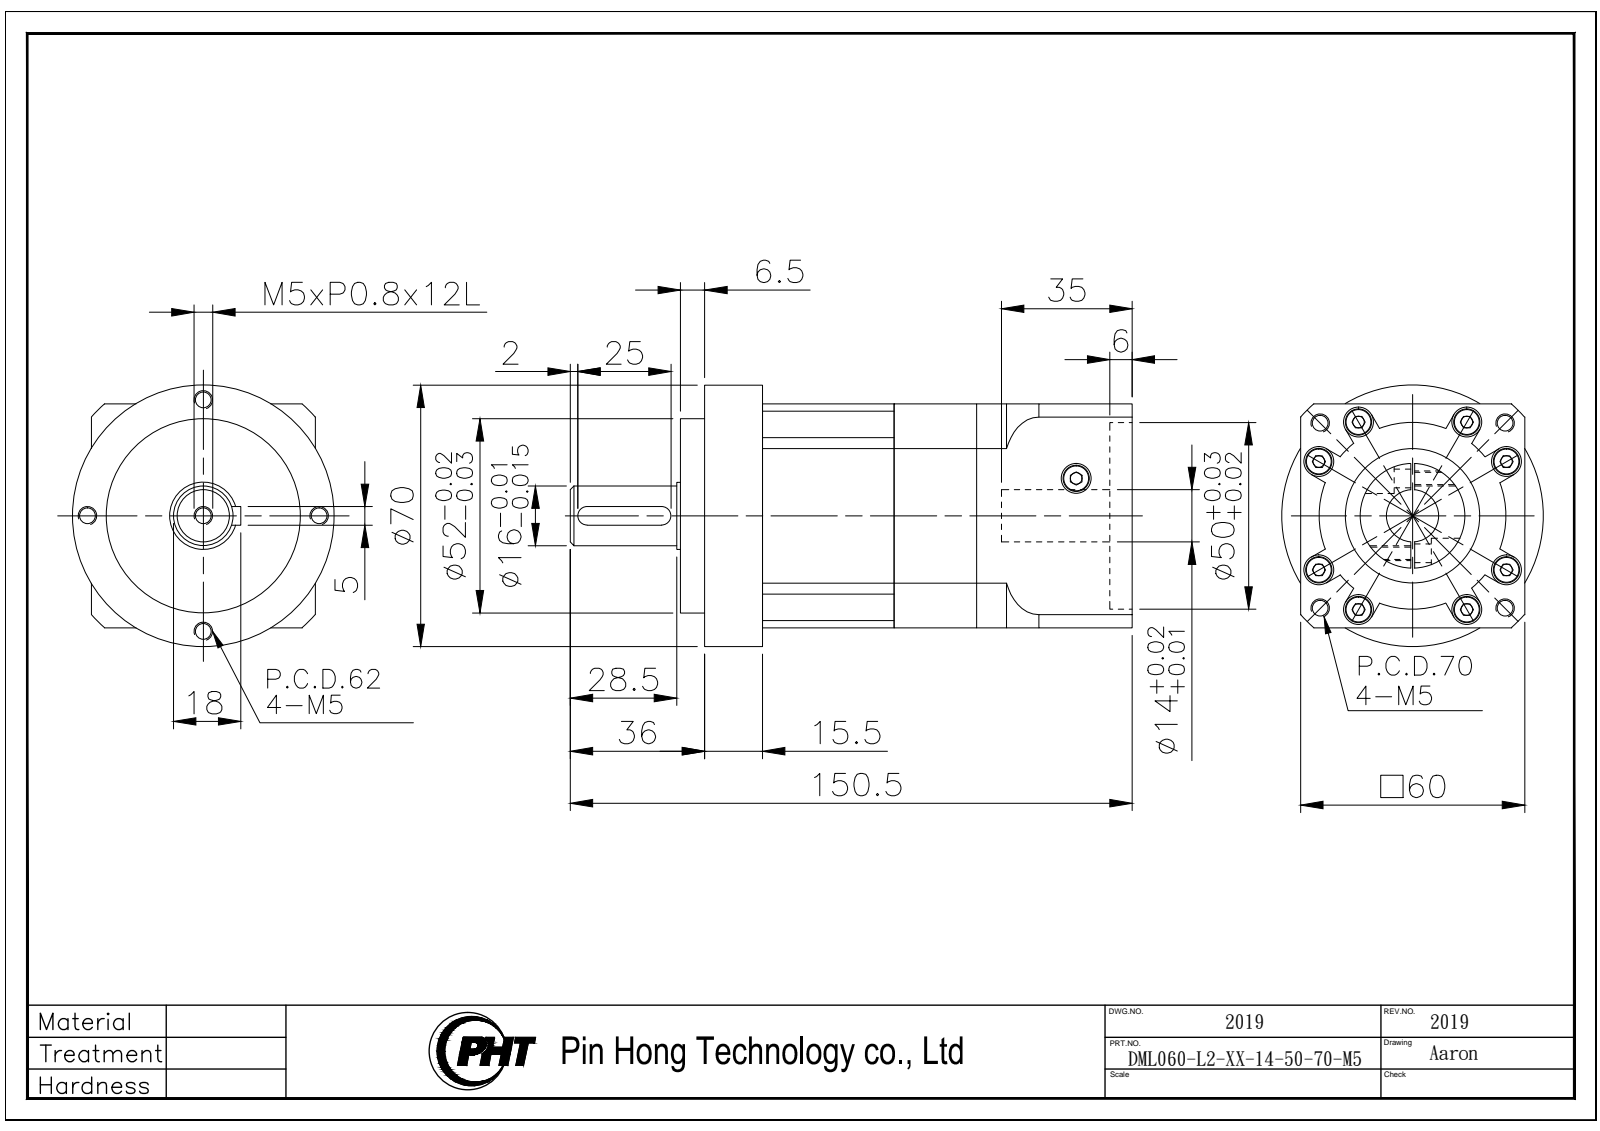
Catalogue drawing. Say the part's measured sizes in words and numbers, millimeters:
The part is named "DML060-L2-XX-14-50-70-M5_2019". Its 3-D file was written by "SolidWorks 2016 (AUTOMOTIVE_DESIGN)". It is 4 solids with 294 faces: 130 planar, 124 cylindrical and 40 other. Overall it measures 150.5 by 70 by 70 millimeters. Its volume is 370 744 cubic millimeters and its surface area 73 760 square millimeters. Round holes: 10 of diameter 8, 9 of diameter 4.2, 8 of diameter 4.5, 1 of diameter 14, 1 of diameter 36. Round bosses or shafts: 8 of diameter 7, 1 of diameter 70, 1 of diameter 52, 1 of diameter 28, 1 of diameter 18, 1 of diameter 16. Partial cylindrical surfaces (rounded edges, fillets, slot ends): 4 of radius 5, 2 of radius 2.5, 1 of radius 25, 1 of radius 40. The main face-to-face distances are 60, 57.35, 22.15, 35.2, 79.35, 57.2, 22, 72.85, 50.7, 15.5. The hole center spacings are 29, 10.26, 15.65, 25.53, 30.05, 39.25, 41.01, 50.9.
